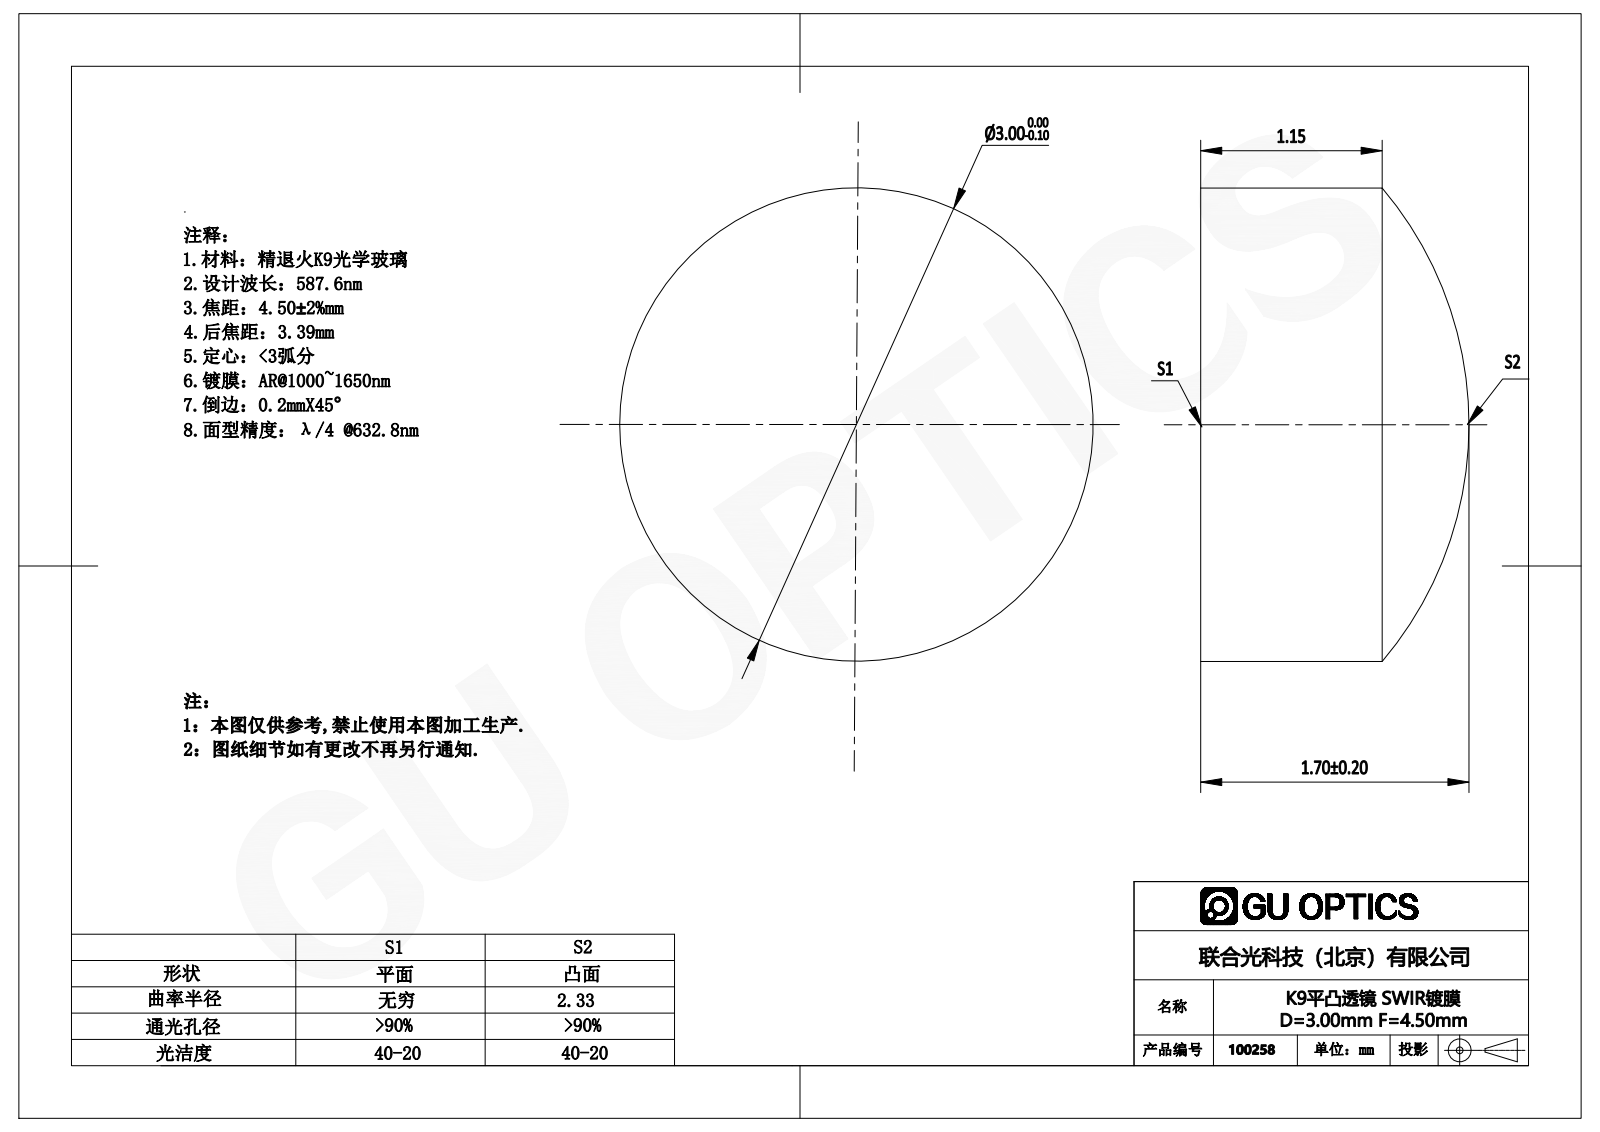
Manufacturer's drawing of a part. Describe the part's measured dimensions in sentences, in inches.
The part is named "100086". Its 3-D file was written by "SolidWorks 2016 (AUTOMOTIVE_DESIGN)". It is 1 solid with 5 faces: 1 planar, 2 cylindrical and 2 other. Overall it measures 0.118 by 0.118 by 0.067 inches. Its volume is 0.001 cubic inches and its surface area 0.04 square inches. Round bosses or shafts: 1 of diameter 0.118.
